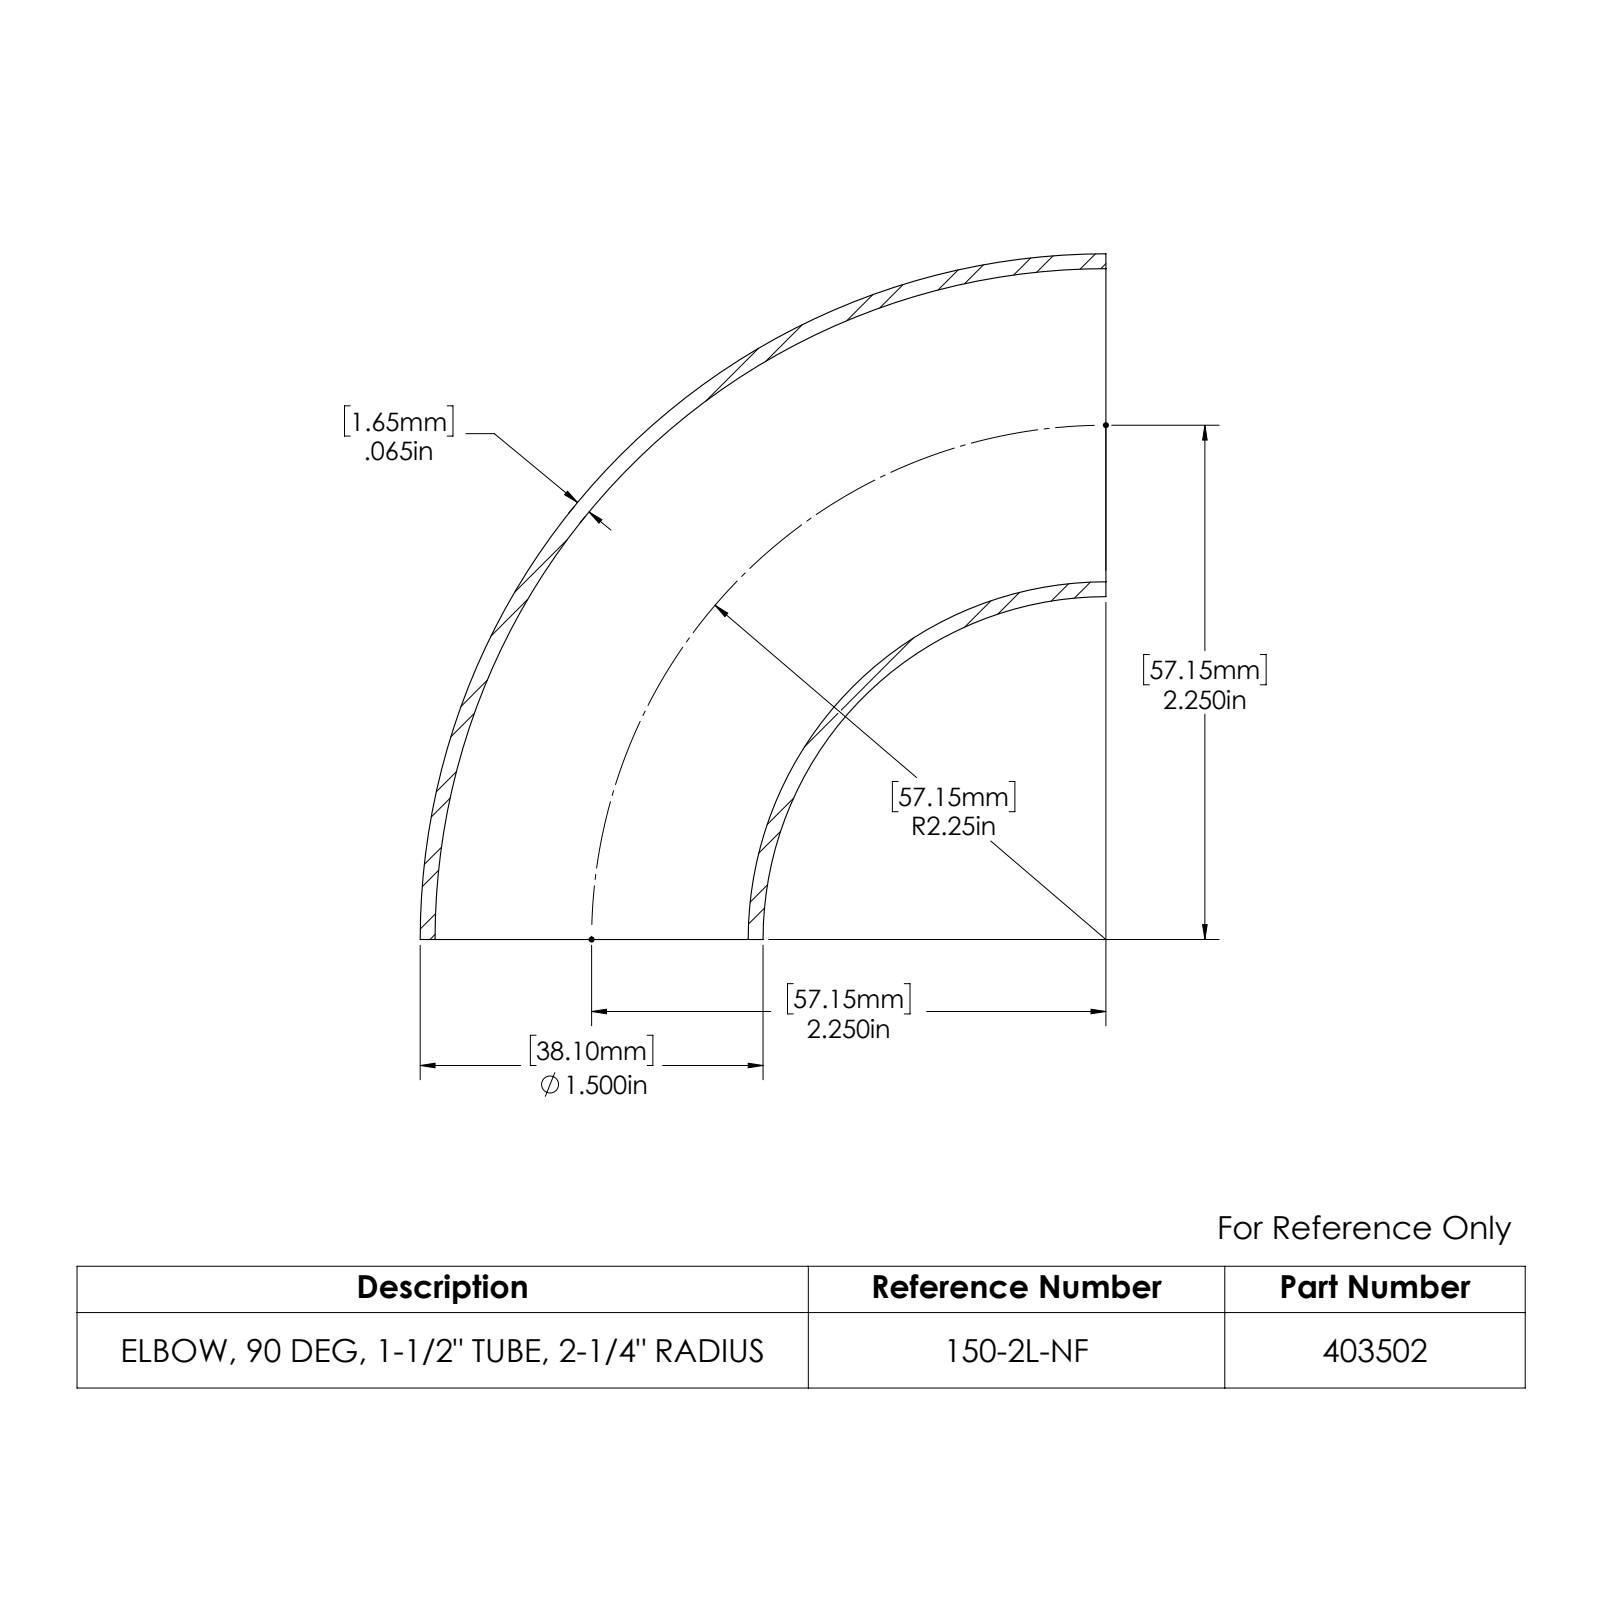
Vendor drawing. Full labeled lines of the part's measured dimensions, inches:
Part name (STEP PRODUCT): 403502
STEP written by: SolidWorks 2022 (AUTOMOTIVE_DESIGN)
Units: inches
Bodies: 1 solid, 6 faces (2 planar, 0 cylindrical, 4 other)
Overall size (bounding box): 3 × 3 × 1.5
Volume: 1.036 in³ · Surface area: 32.45 in²
